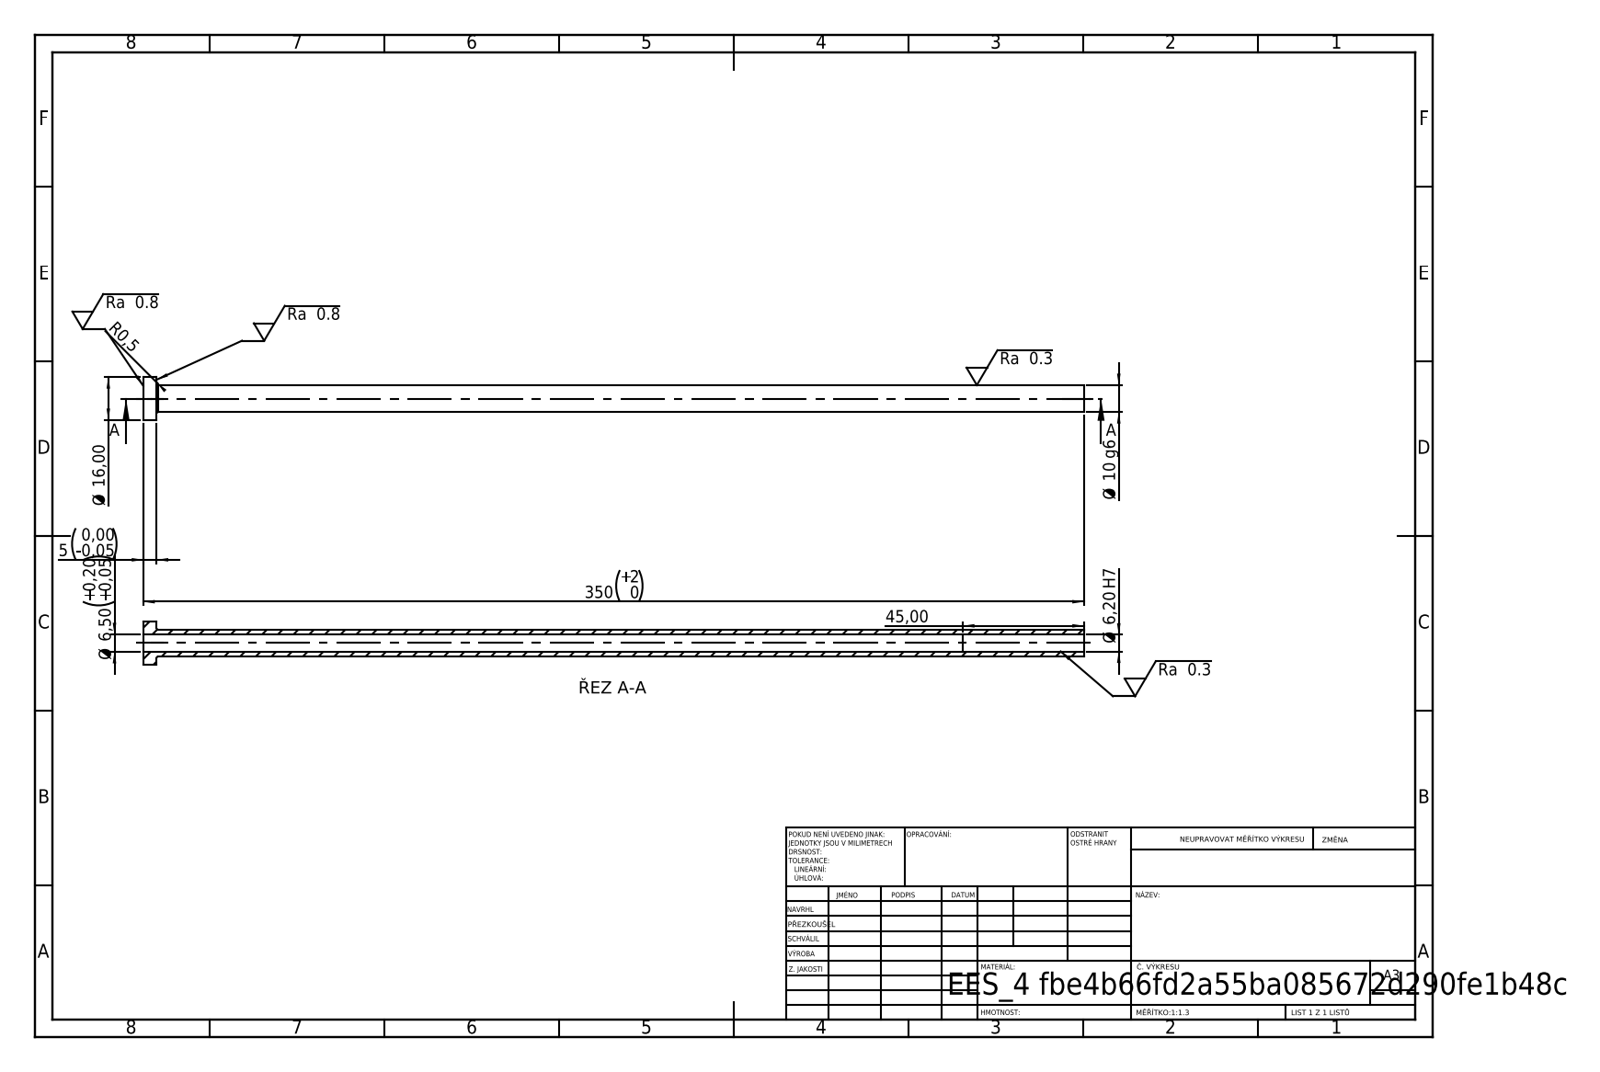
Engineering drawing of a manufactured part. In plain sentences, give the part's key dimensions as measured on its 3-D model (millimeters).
Its 3-D file was written by "SolidWorks 2019 (CONFIG_CONTROL_DESIGN)". It is 1 solid with 14 faces: 4 planar, 8 cylindrical and 2 other. Overall it measures 350 by 16 by 16 millimeters. Its volume is 16 624 cubic millimeters and its surface area 18 530 square millimeters. Round holes: 1 of diameter 6.2, 1 of diameter 6.5. Round bosses or shafts: 1 of diameter 16, 1 of diameter 10. The main face-to-face distances are 5, 350, 345, 305, 300, 45.
